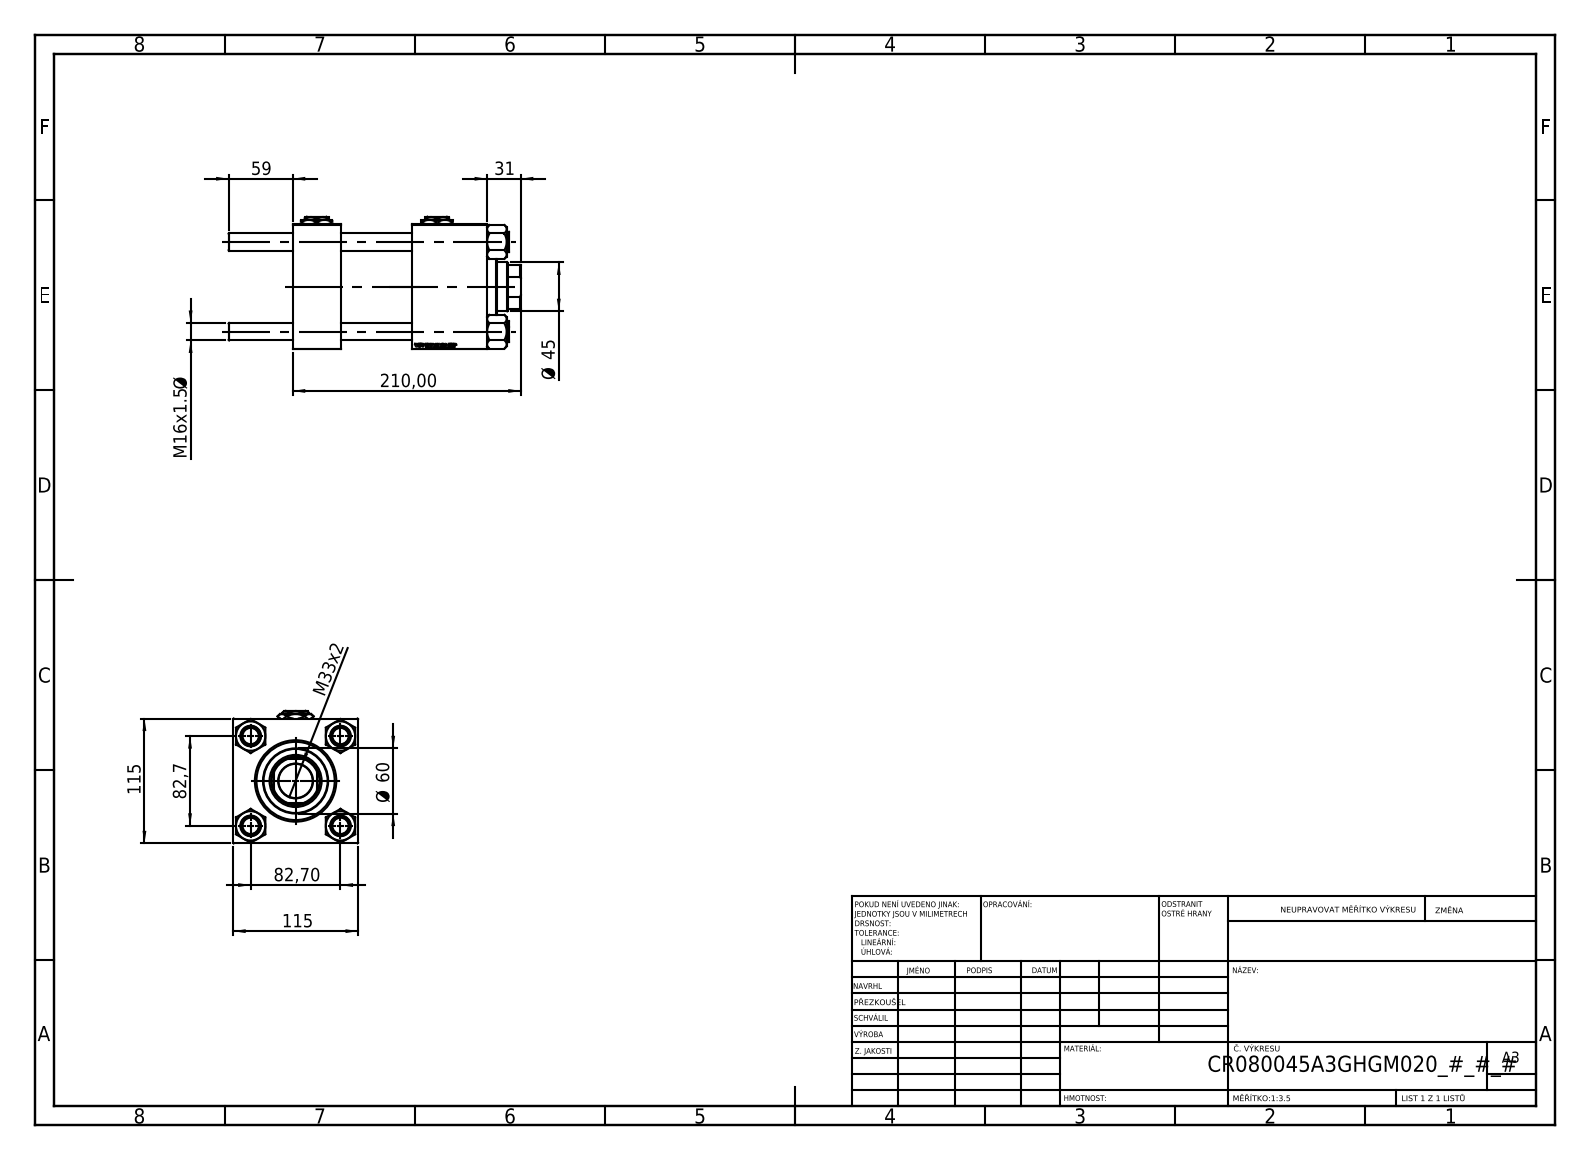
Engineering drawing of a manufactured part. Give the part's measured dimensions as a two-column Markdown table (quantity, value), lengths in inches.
| quantity | value |
| --- | --- |
| part name | NUT_M5; Zatka_pro_OIL_PORT; V215CR_VCP; V215CR_BODY_A (+2 more) |
| STEP written by | SolidWorks 2019 (CONFIG_CONTROL_DESIGN) |
| units | inches |
| bodies | 13 solids, 1281 faces (615 planar, 88 cylindrical, 578 other) |
| overall size | 10.591 × 4.803 × 4.528 |
| volume | 115 in³ |
| surface area | 475.8 in² |
| round holes (diameter × count) | 0.63 × 4, 0.276 × 2, 1.041 × 2, 1.378 × 2, 1.24 × 1, 1.772 × 1, 1.89 × 1, 2.402 × 1, 2.835 × 1, 3.15 × 1 |
| round bosses / shafts (diameter × count) | 0.748 × 4, 3.386 × 1, 2.362 × 1 |
| partial cylindrical surfaces (radius × count) | 0.866 × 1 |
| main face-to-face distances | 4.528, 1.732, 7.047, 5.315, 4.331, 2.717, 2.598, 0.787, 3.504, 5.917 |
| hole center spacings | 2.302, 3.256, 4.605, 4.37 |
